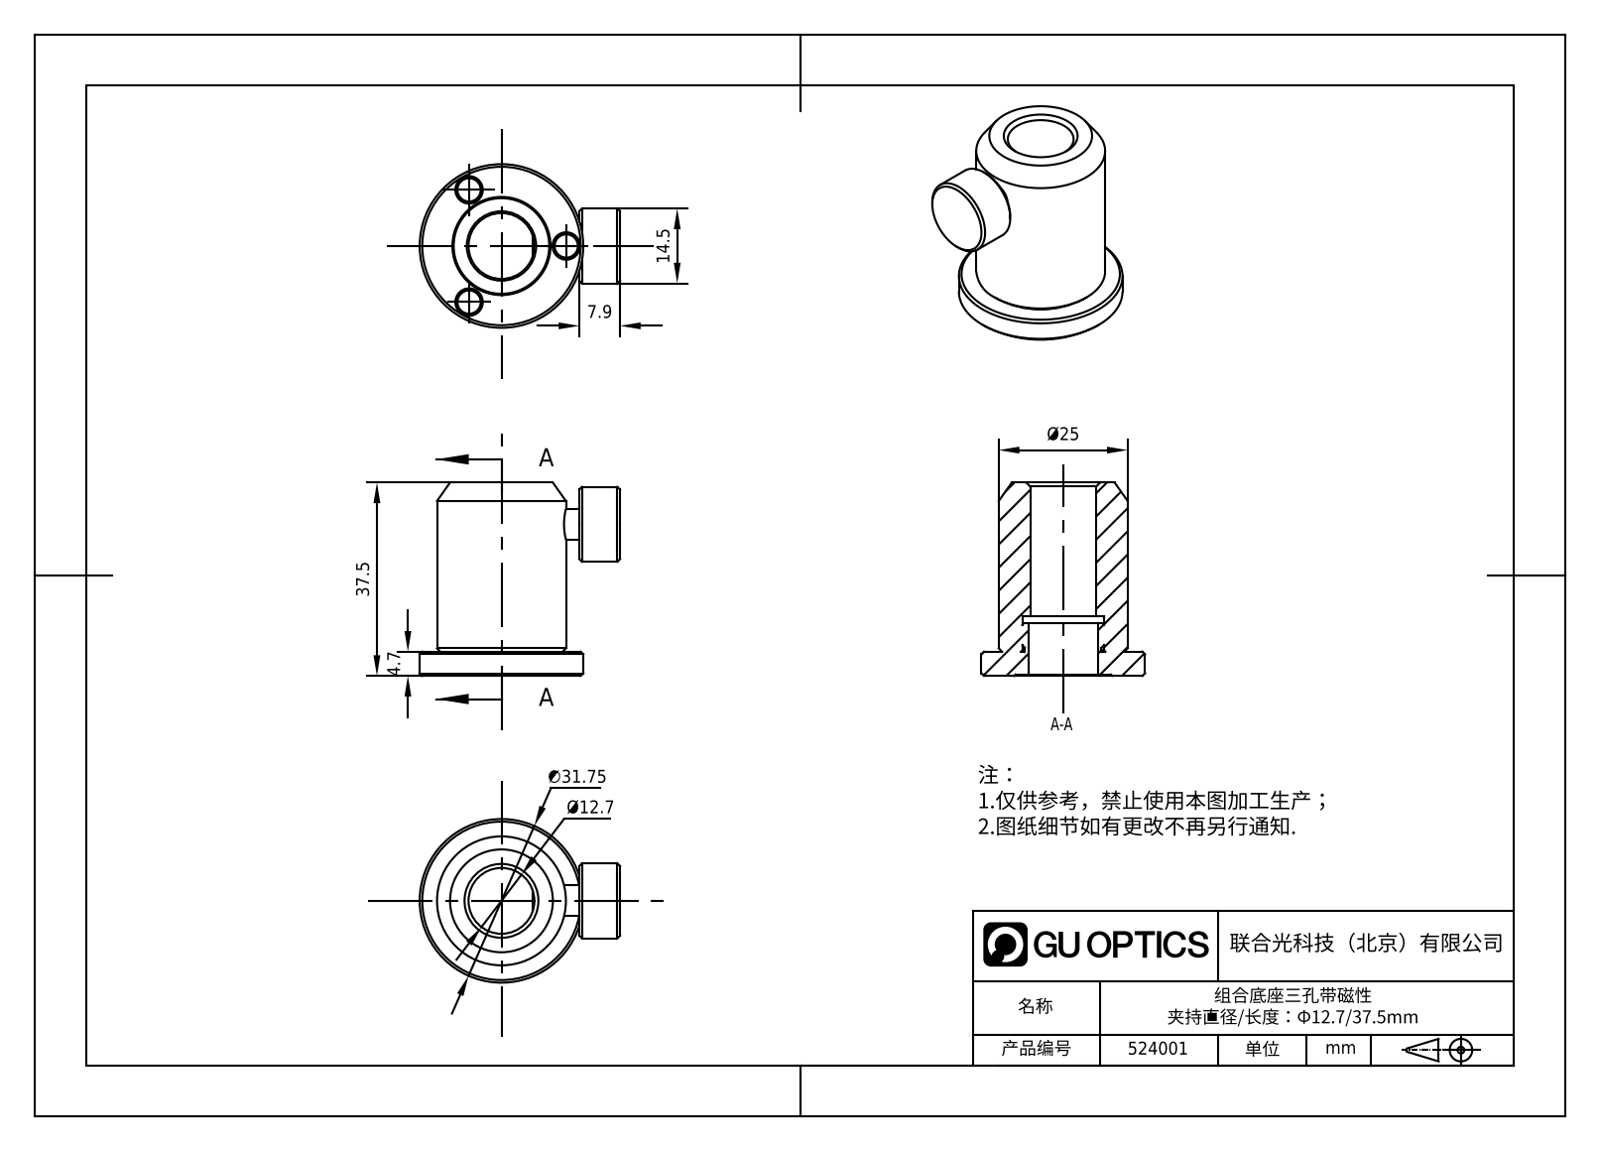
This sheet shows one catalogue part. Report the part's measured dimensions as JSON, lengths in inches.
{"part_name": "524001", "step_written_by": "SolidWorks 2016 (AUTOMOTIVE_DESIGN)", "units": "inches", "bodies": {"solids": 5, "faces": 90, "planar": 19, "cylindrical": 31, "other": 40}, "overall_size": [1.531, 1.476, 1.25], "volume_in3": 0.958, "surface_area_in2": 11.67, "round_holes": [[0.19, 3], [0.236, 1], [0.503, 1], [0.53, 1], [0.625, 1]], "round_bosses_or_shafts": [[0.187, 3], [1.25, 1], [0.985, 1], [0.585, 1], [0.571, 1]], "partial_cylinders_radius": [[0.313, 1]], "face_to_face_distances": [0.185, 1.476, 1.291, 0.175, 1.466, 0.311, 0.455, 0.445, 0.27, 1.021], "hole_center_spacings": [0.857, 0.495, 0.495]}
